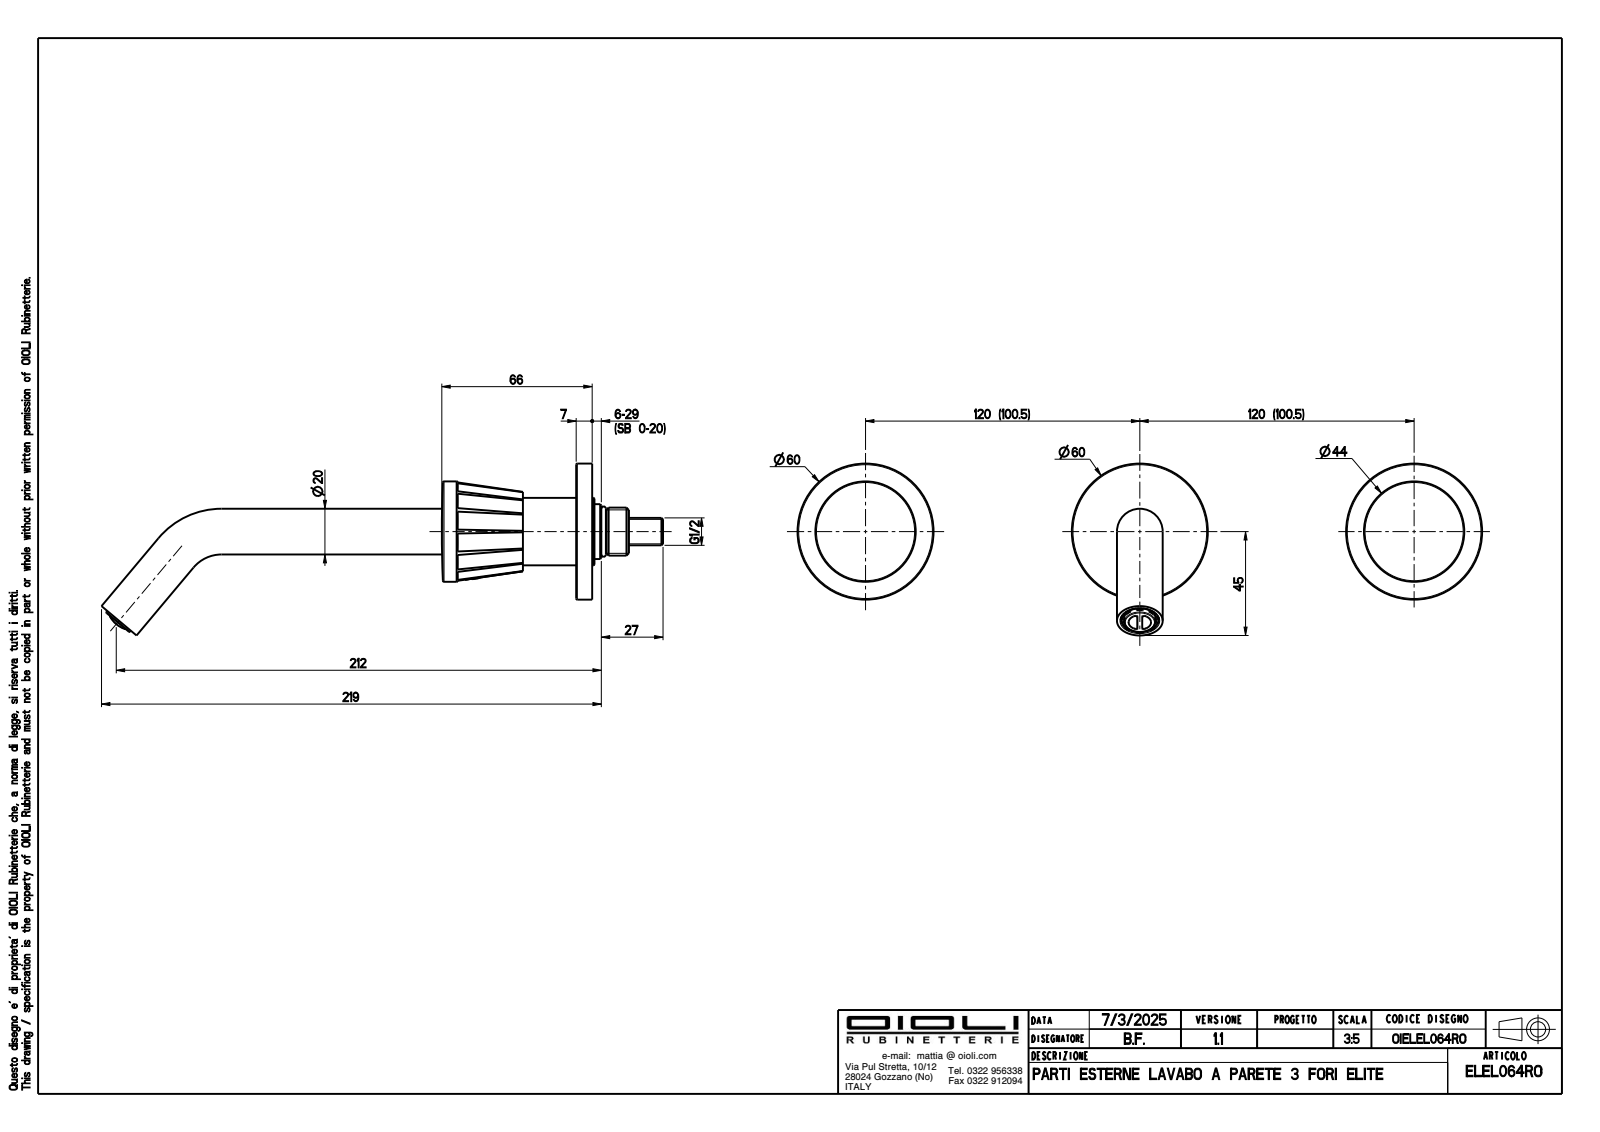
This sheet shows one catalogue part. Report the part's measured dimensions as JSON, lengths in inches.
{"part_name": "OIBR00632; OIBR00950; OIBR00633; OIBR00689 (+6 more)", "step_written_by": "CREO PARAMETRIC BY PTC INC, 2024493 (CONFIG_CONTROL_DESIGN)", "units": "inches", "bodies": {"solids": 15, "faces": 1233, "planar": 725, "cylindrical": 209, "other": 299}, "overall_size": [17.459, 11.791, 3.835], "volume_in3": 6.392, "surface_area_in2": 141.6, "round_holes": [[0.551, 4], [0.165, 3], [0.157, 2], [0.209, 2], [0.256, 2], [0.276, 2], [0.61, 2], [0.906, 2], [1.063, 2], [1.181, 2], [1.299, 2], [2.256, 2]], "round_bosses_or_shafts": [[0.65, 4], [2.343, 3], [0.197, 3], [1.728, 2], [1.417, 2], [1.161, 2], [0.945, 2], [0.787, 2]], "partial_cylinders_radius": [[0.004, 24], [0.035, 8], [0.024, 4], [0.018, 3], [0.295, 2], [0.098, 1], [0.265, 1], [0.294, 1]], "face_to_face_distances": [0.955, 0.079, 0.059, 0.773, 0.182, 0.852, 0.103, 0.044, 0.832, 0.911], "hole_center_spacings": [4.724, 6.128, 7.611, 9.449, 13.663]}
